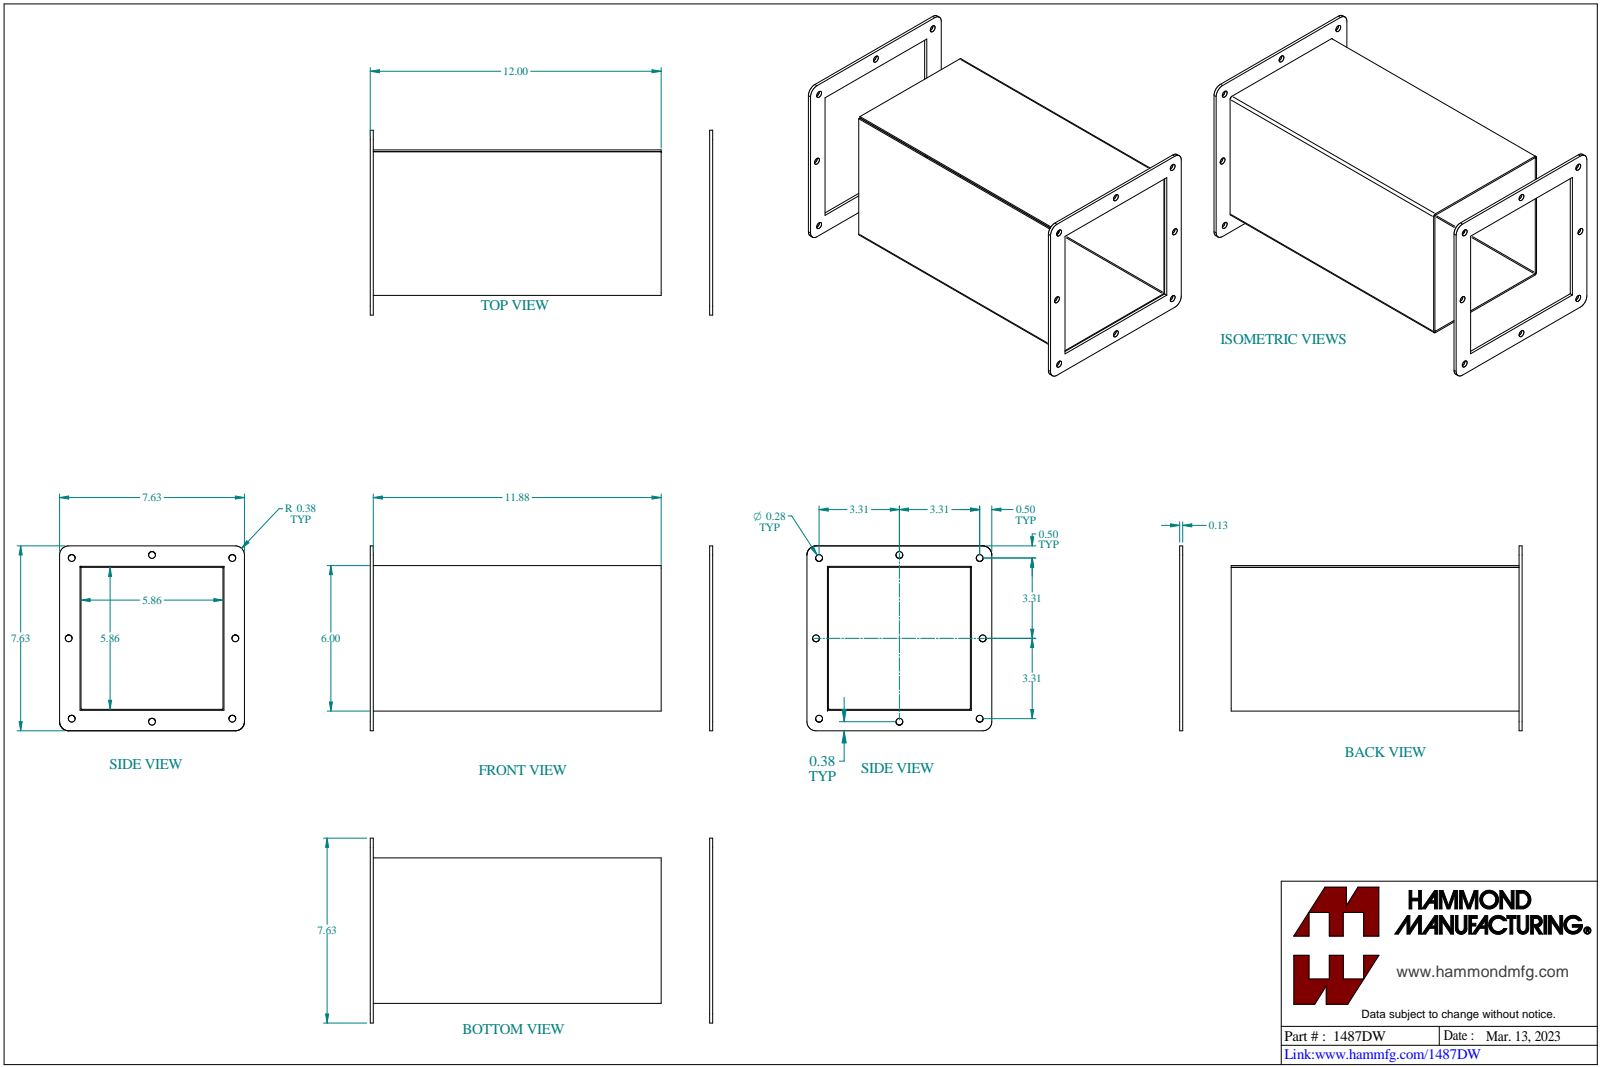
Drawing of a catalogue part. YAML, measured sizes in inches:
part_name: "1487DW"
step_written_by: "SolidWorks 2023 (CONFIG_CONTROL_DESIGN)"
units: inches
bodies: {solids: 4, faces: 112, planar: 42, cylindrical: 70, other: 0}
overall_size: [14.25, 7.626, 7.625]
volume: 28.49
surface_area: 720.7
round_holes:
  - {diameter: 0.281, count: 16}
partial_cylinders:
  - {radius: 0.375, count: 8}
  - {radius: 0.25, count: 4}
  - {radius: 0.036, count: 3}
  - {radius: 0.108, count: 3}
face_to_face_distances: [0.072, 5.928, 6, 5.856, 0.125, 14, 0.25, 0.125, 14.125, 14.25]
hole_center_spacings: [7.519, 3.315, 3.315, 6.625, 6.875, 3.314, 3.316, 4.861]
